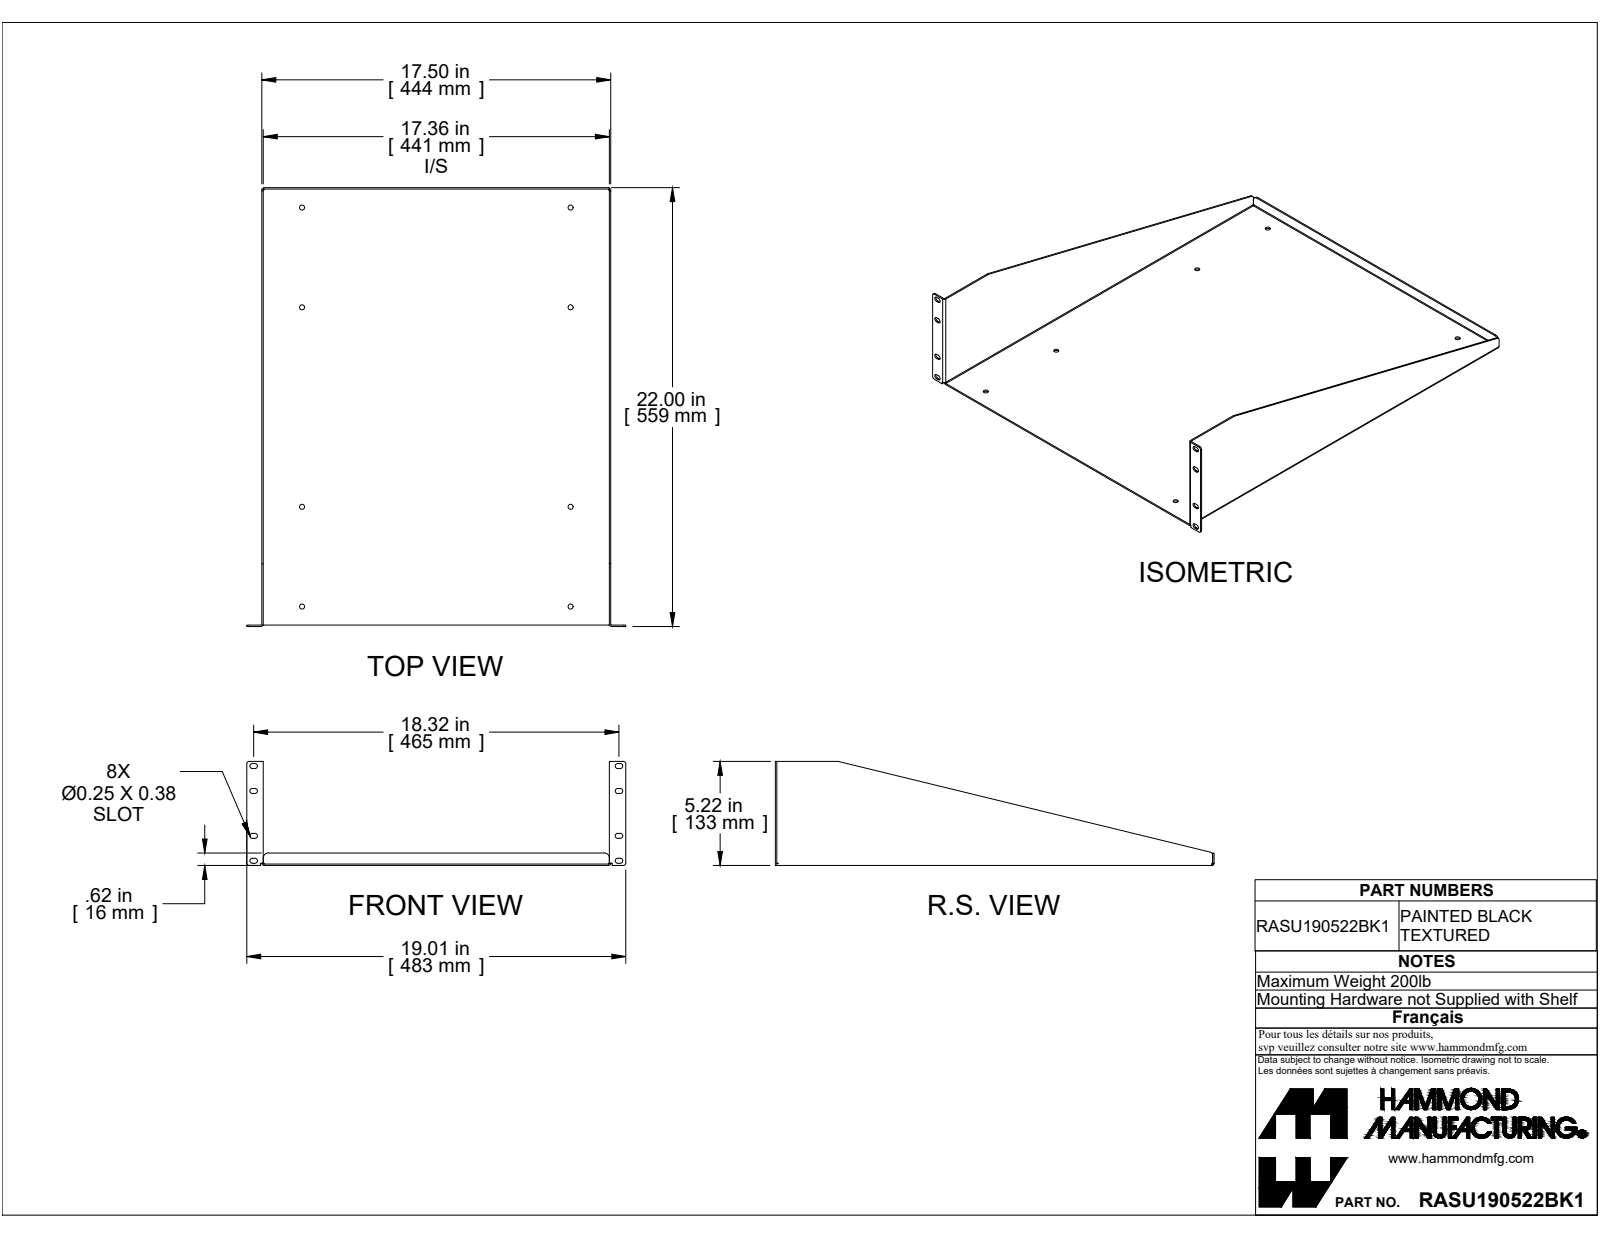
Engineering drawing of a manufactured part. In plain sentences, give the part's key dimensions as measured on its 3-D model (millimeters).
The part is named "RASU190522BK1". Its 3-D file was written by "SolidWorks 2019 (CONFIG_CONTROL_DESIGN)". It is 1 solid with 104 faces: 56 planar, 44 cylindrical and 4 other. Overall it measures 558.8 by 482.8 by 132.5 millimeters. Its volume is 634 300 cubic millimeters and its surface area 698 700 square millimeters. Round holes: 8 of diameter 6.4. Partial cylindrical surfaces (rounded edges, fillets, slot ends): 20 of radius 3.2, 5 of radius 0.9, 5 of radius 2.7, 3 of radius 1.4, 2 of radius 6.4. The main face-to-face distances are 1.8, 442.7, 440.8, 444.5, 555.1, 557, 1.8, 557, 558.8, 15.9. The hole center spacings are 127, 342.1, 364.9, 381, 512, 254, 426.1, 508.
